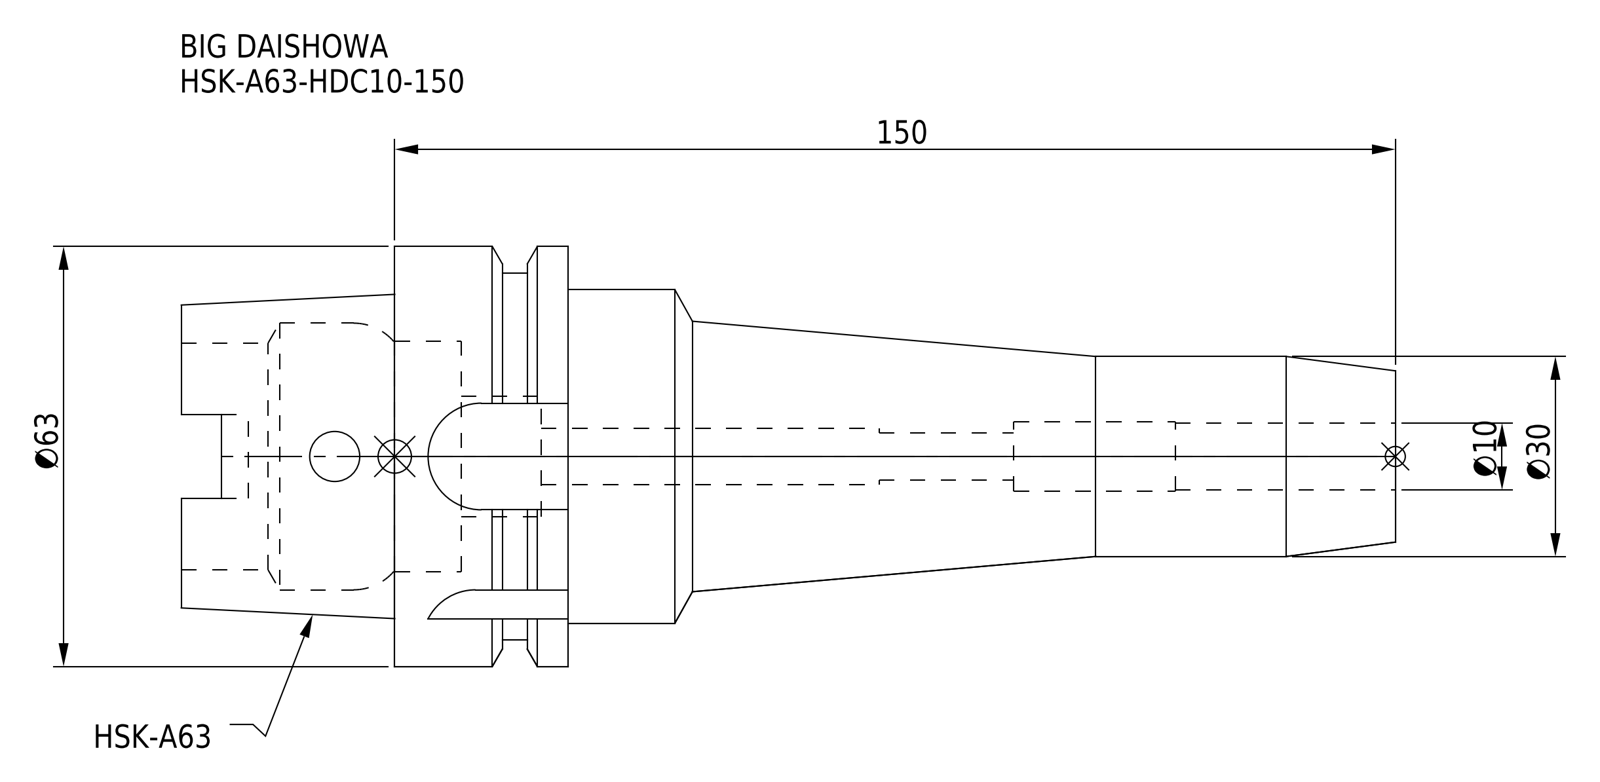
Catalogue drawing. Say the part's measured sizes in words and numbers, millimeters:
The part is named "HSK-A63-HDC10-150". Its 3-D file was written by "CREO PARAMETRIC BY PTC INC, 2016380 (AUTOMOTIVE_DESIGN)". It is 1 solid with 100 faces: 39 planar, 41 cylindrical and 20 other. Overall it measures 182 by 63 by 63 millimeters. Its volume is 198 931 cubic millimeters and its surface area 38 569 square millimeters. Round holes: 1 of diameter 7, 1 of diameter 7.5, 1 of diameter 8.4, 1 of diameter 10, 1 of diameter 10.5, 1 of diameter 18, 1 of diameter 34, 1 of diameter 34.5, 1 of diameter 40. Round bosses or shafts: 1 of diameter 63, 1 of diameter 55, 1 of diameter 50, 1 of diameter 30. Partial cylindrical surfaces (rounded edges, fillets, slot ends): 4 of radius 2.88, 4 of radius 8. The main face-to-face distances are 26, 16.05, 9.95, 124, 140.05, 150, 182, 58, 41.95, 32.
